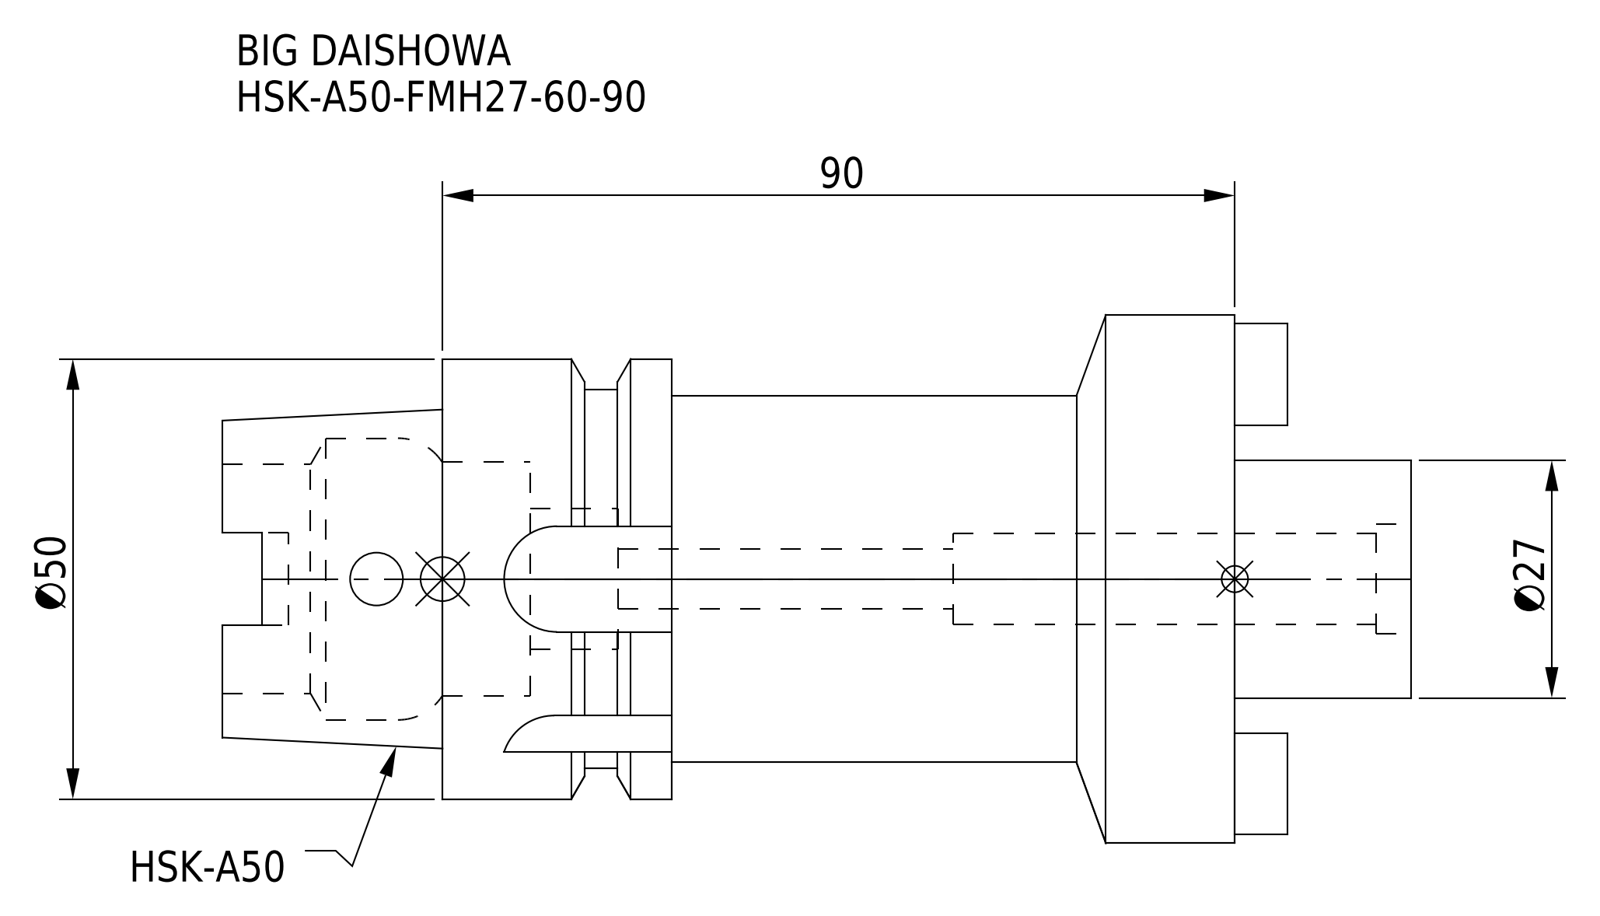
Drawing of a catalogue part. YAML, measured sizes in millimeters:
part_name: "HSK-A50-FMH27-60-90"
step_written_by: "CREO PARAMETRIC BY PTC INC, 2016380 (AUTOMOTIVE_DESIGN)"
units: millimeters
bodies: {solids: 1, faces: 108, planar: 49, cylindrical: 43, other: 16}
overall_size: [135, 60, 60]
volume: 167269
surface_area: 31600
round_holes:
  - {diameter: 6, count: 1}
  - {diameter: 6.8, count: 1}
  - {diameter: 10.3, count: 1}
  - {diameter: 12.5, count: 1}
  - {diameter: 16, count: 1}
  - {diameter: 26, count: 1}
  - {diameter: 26.6, count: 1}
  - {diameter: 32, count: 1}
round_bosses_or_shafts:
  - {diameter: 60, count: 1}
  - {diameter: 50, count: 1}
  - {diameter: 43, count: 1}
  - {diameter: 41.6, count: 1}
  - {diameter: 27, count: 1}
partial_cylinders:
  - {radius: 2.38, count: 4}
  - {radius: 6, count: 4}
face_to_face_distances: [90, 64, 26, 20, 84, 110, 100.05, 80.05, 16.05, 9.95]
